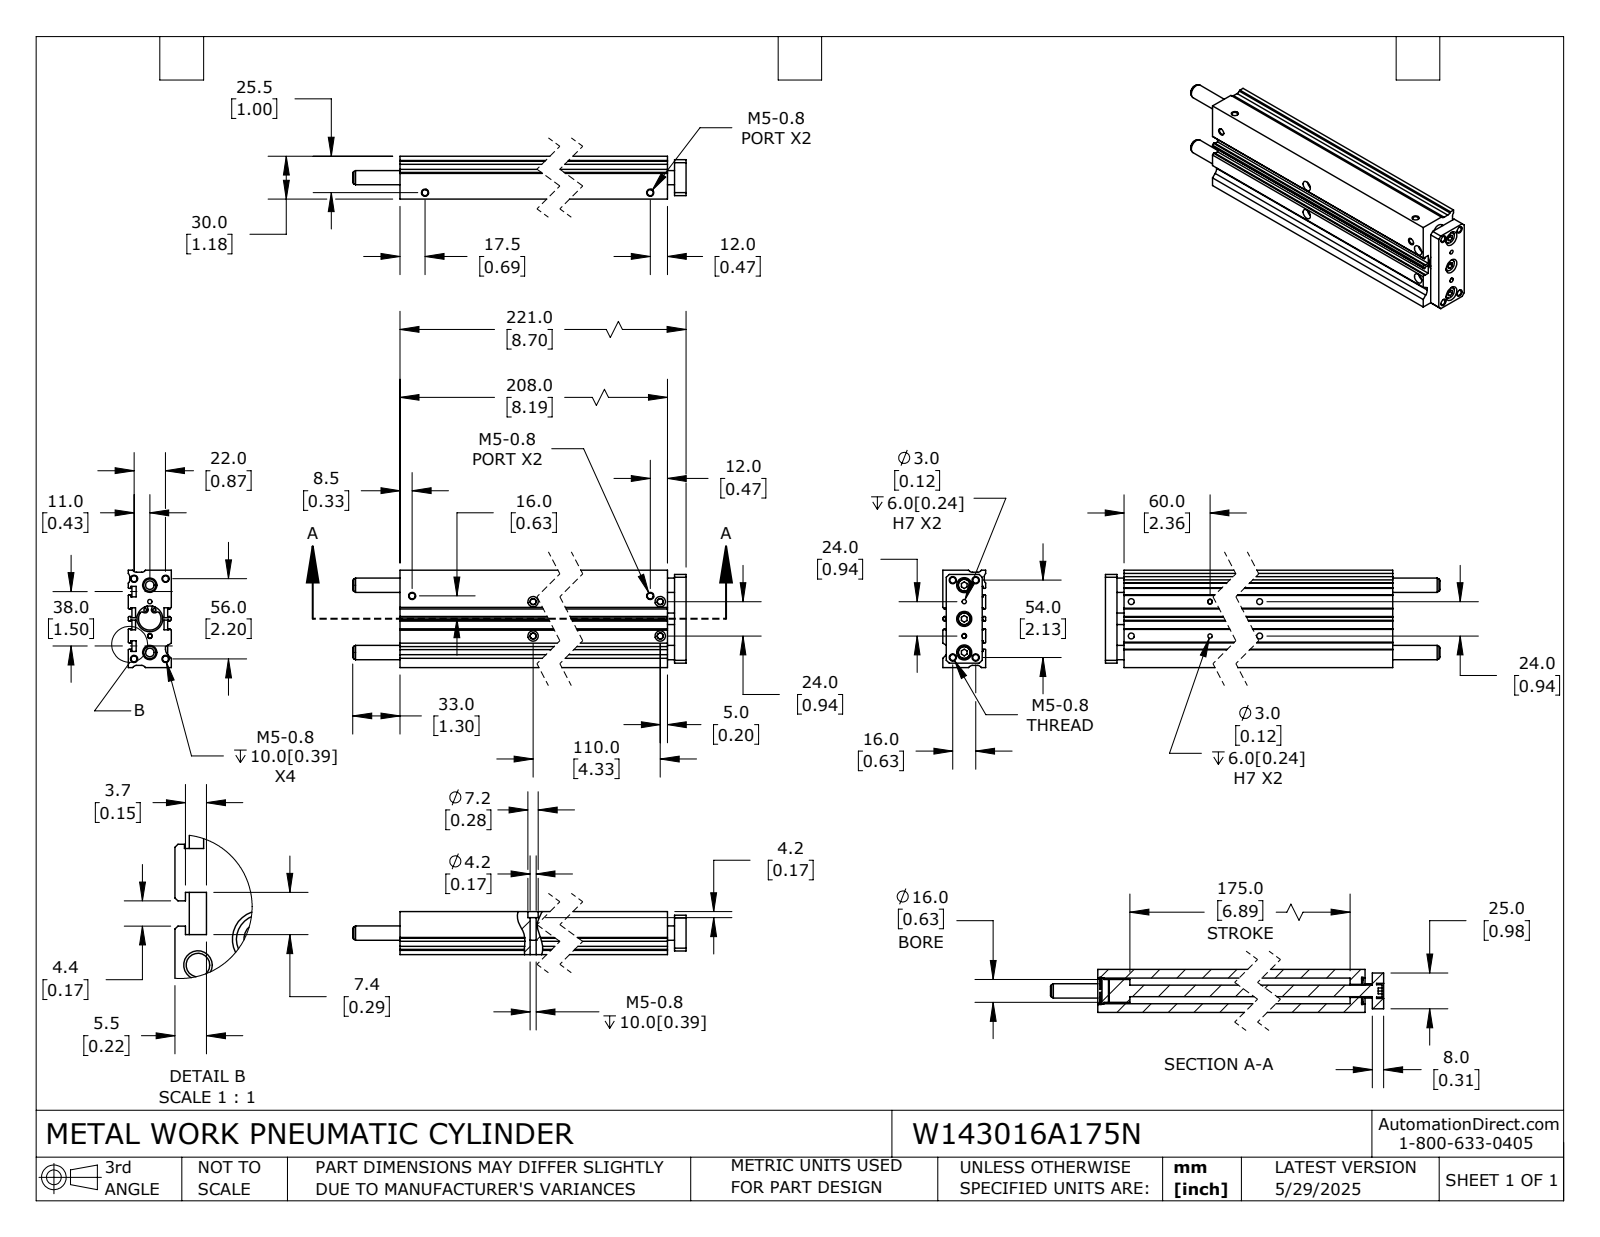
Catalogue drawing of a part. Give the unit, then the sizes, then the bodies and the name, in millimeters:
Units: millimetres
Overall size (bounding box): 254 × 68 × 30
Round holes (diameter × count): ⌀4.13 ×16, ⌀2 ×4, ⌀3 ×4, ⌀4.2 ×4, ⌀7.2 ×4, ⌀10.5 ×3, ⌀10 ×2, ⌀9.2 ×1, ⌀15.7 ×1, ⌀18 ×1
Round bosses / shafts (diameter × count): ⌀8.5 ×3, ⌀19 ×2, ⌀16 ×1, ⌀8 ×1
Partial cylindrical surfaces — rounded edges, fillets, slot ends (radius × count): R3 ×6, R1.5 ×4, R1.58 ×4, R2.07 ×4, R5 ×1
Main face-to-face distances: 30, 5, 25, 68, 1.5, 5.5, 0.5, 33.15, 24.5, 19.5
Hole centre spacings: 3.16, 6.62, 6.95, 8.73, 11.88, 17, 17.6, 18.46
Volume: 347 322 mm³ · Surface area: 117 730 mm²
Bodies: 5 solids, 344 faces (169 planar, 137 cylindrical, 38 other)
Part name (STEP PRODUCT): W143016A175N; W143016A175N_BODY; W143016A175N_ROD
STEP written by: SolidWorks 2024 (CONFIG_CONTROL_DESIGN)
